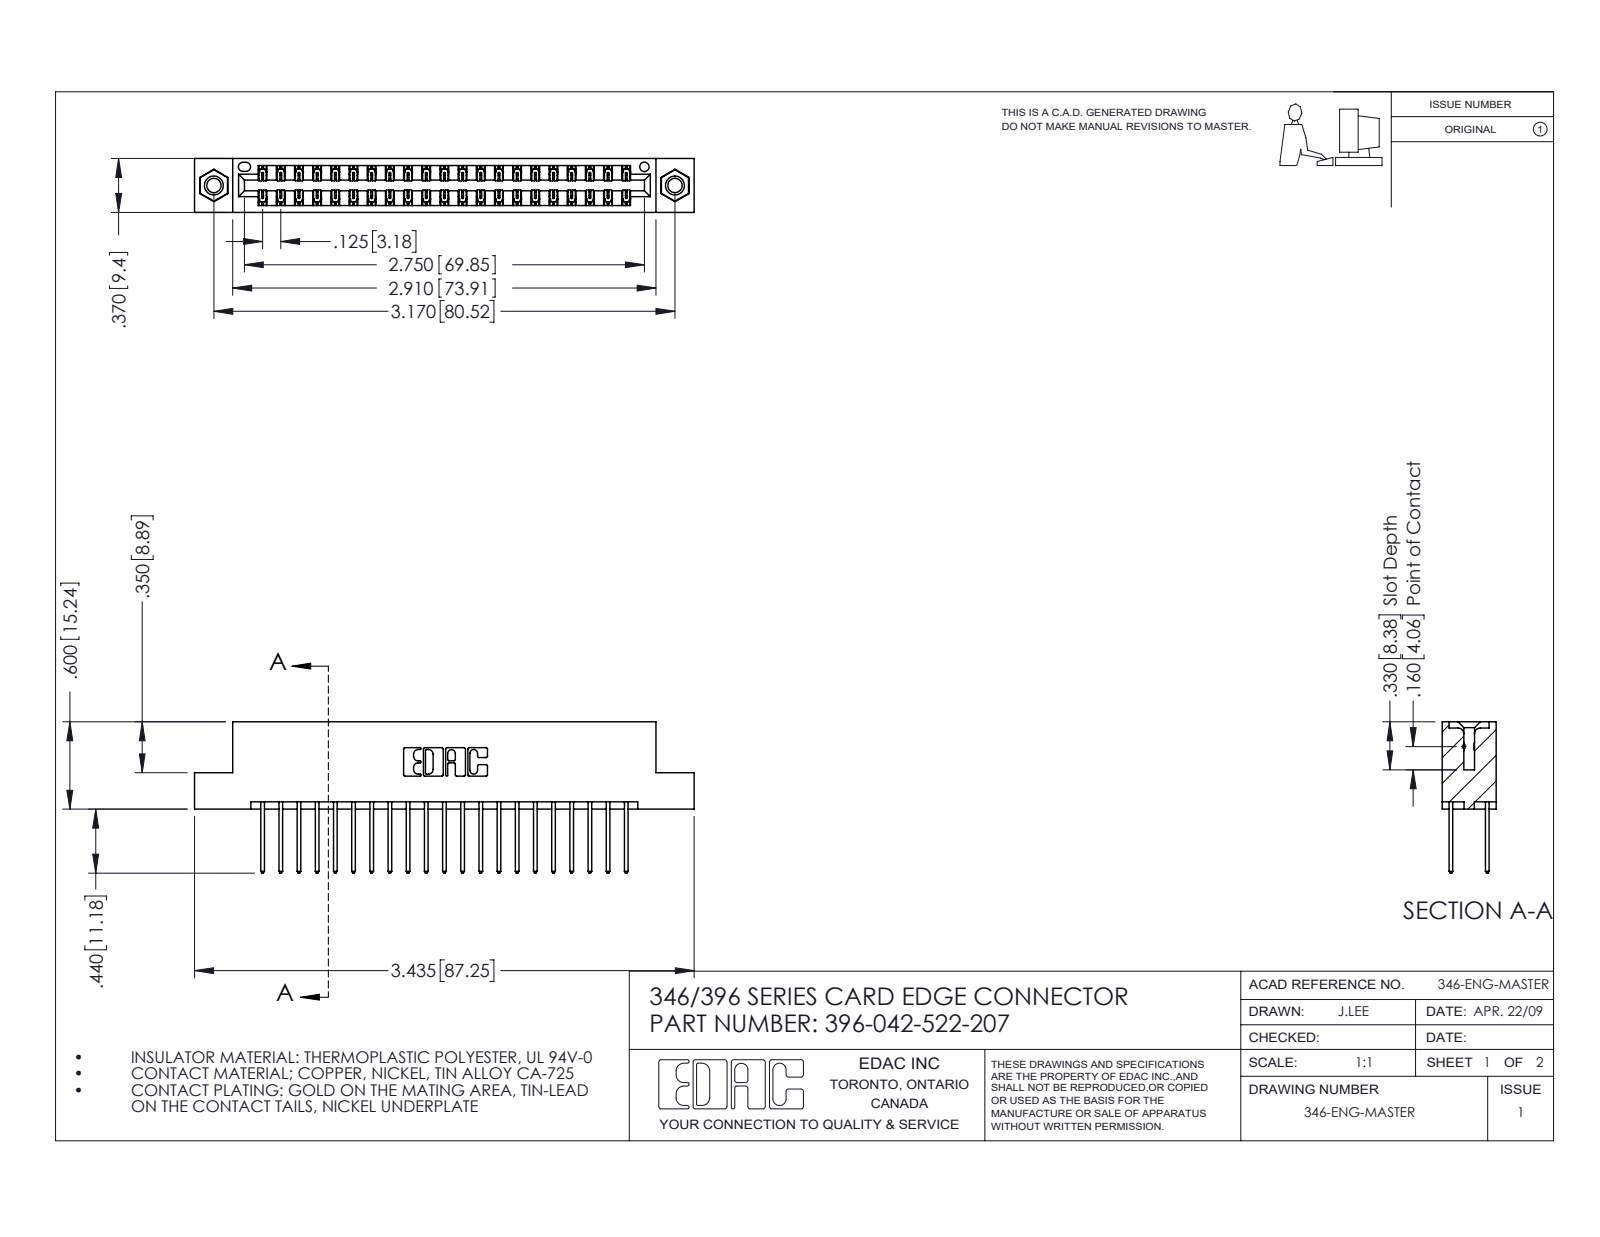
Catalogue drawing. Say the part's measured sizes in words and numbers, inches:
The part is named "346 Part_Flush Mounting Lugs - 0.156 Dia-TI; 345-292-001_345-293-122; 396-042-522-207; 345-250-001_345-250-005-103". Its 3-D file was written by "SolidWorks 2016 (CONFIG_CONTROL_DESIGN)". It is 45 solids with 2366 faces: 1578 planar, 772 cylindrical and 16 other. Overall it measures 3.435 by 1.04 by 0.37 inches. Its volume is 0.515 cubic inches and its surface area 18.29 square inches. Round holes: 2 of diameter 0.098, 2 of diameter 0.125, 2 of diameter 0.156, 1 of diameter 0.064. Round bosses or shafts: 2 of diameter 0.155. Partial cylindrical surfaces (rounded edges, fillets, slot ends): 63 of radius 0.006, 42 of radius 0.01, 22 of radius 0.01, 6 of radius 0.007, 6 of radius 0.031, 3 of radius 0.026, 2 of radius 0.014, 2 of radius 0.022. The main face-to-face distances are 0.048, 0.322, 0.25, 0.37, 0.072, 0.298, 0.025, 0.275, 0.148, 0.222. The hole center spacings are 0.246, 2.963, 3.17.
